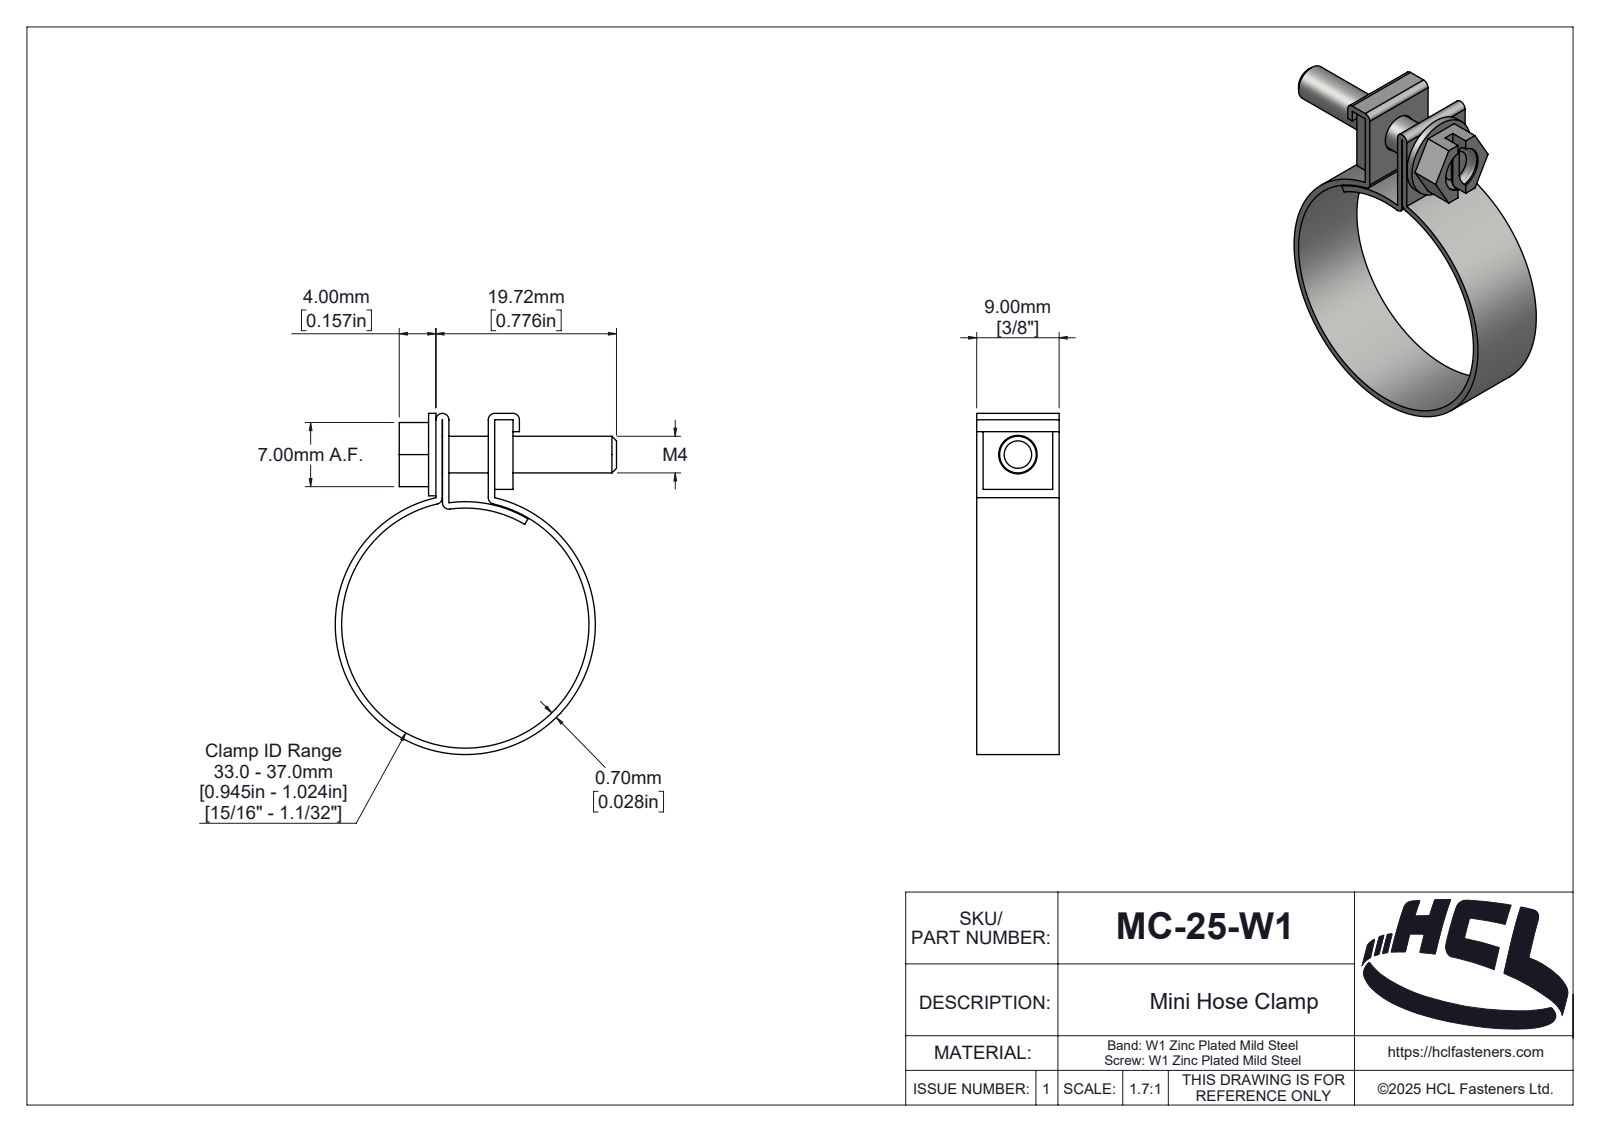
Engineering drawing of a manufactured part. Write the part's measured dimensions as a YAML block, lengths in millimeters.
part_name: "MC-25-W1"
step_written_by: "SolidWorks 2025 (AUTOMOTIVE_DESIGN)"
units: millimeters
bodies: {solids: 3, faces: 170, planar: 38, cylindrical: 79, other: 53}
overall_size: [37.24, 30.71, 9]
volume: 1235
surface_area: 3007
round_holes:
  - {diameter: 4.2, count: 1}
  - {diameter: 5, count: 1}
  - {diameter: 27, count: 1}
round_bosses_or_shafts:
  - {diameter: 28.4, count: 1}
  - {diameter: 9, count: 1}
  - {diameter: 4, count: 1}
partial_cylinders:
  - {radius: 0.7, count: 5}
  - {radius: 0.2, count: 1}
  - {radius: 0.71, count: 1}
  - {radius: 0.81, count: 1}
  - {radius: 1.01, count: 1}
  - {radius: 1.06, count: 1}
  - {radius: 1.28, count: 1}
  - {radius: 1.81, count: 1}
face_to_face_distances: [0.7, 5, 0.72, 5.72, 6.42, 7, 9, 2, 2.7, 8.42]
